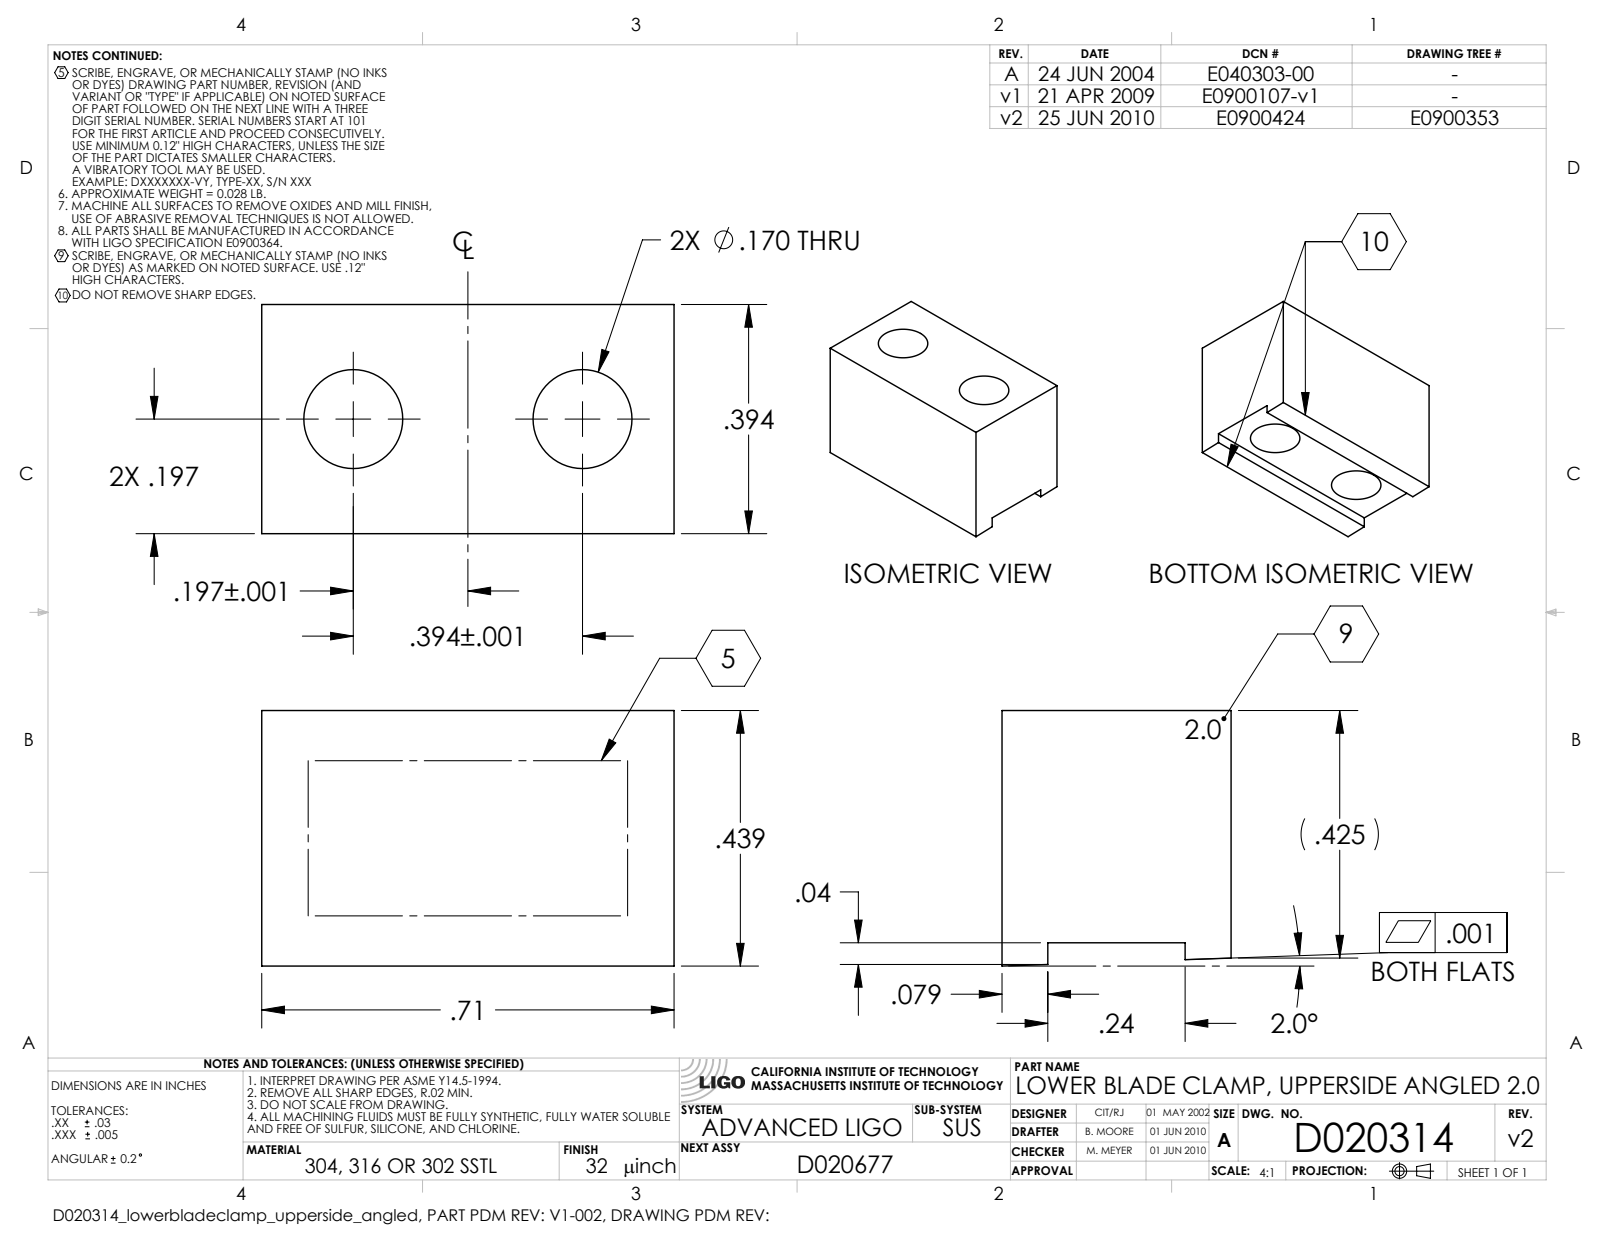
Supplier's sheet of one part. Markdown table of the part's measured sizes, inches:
| quantity | value |
| --- | --- |
| part name | D020314-v2_aLIGO_SUS_HSTS_Lower Blade Clamp, Upper SIde, Angled 2.0 |
| STEP written by | SolidWorks 2009 (CONFIG_CONTROL_DESIGN) |
| units | inches |
| bodies | 1 solid, 14 faces (10 planar, 4 cylindrical, 0 other) |
| overall size | 0.709 × 0.439 × 0.394 |
| volume | 0.097 in³ |
| surface area | 1.878 in² |
| round holes (diameter × count) | 0.17 × 2 |
| main face-to-face distances | 0.394, 0.709, 0.399, 0.079, 0.315, 0.315, 0.236, 0.079 |
| hole center spacings | 0.394 |
